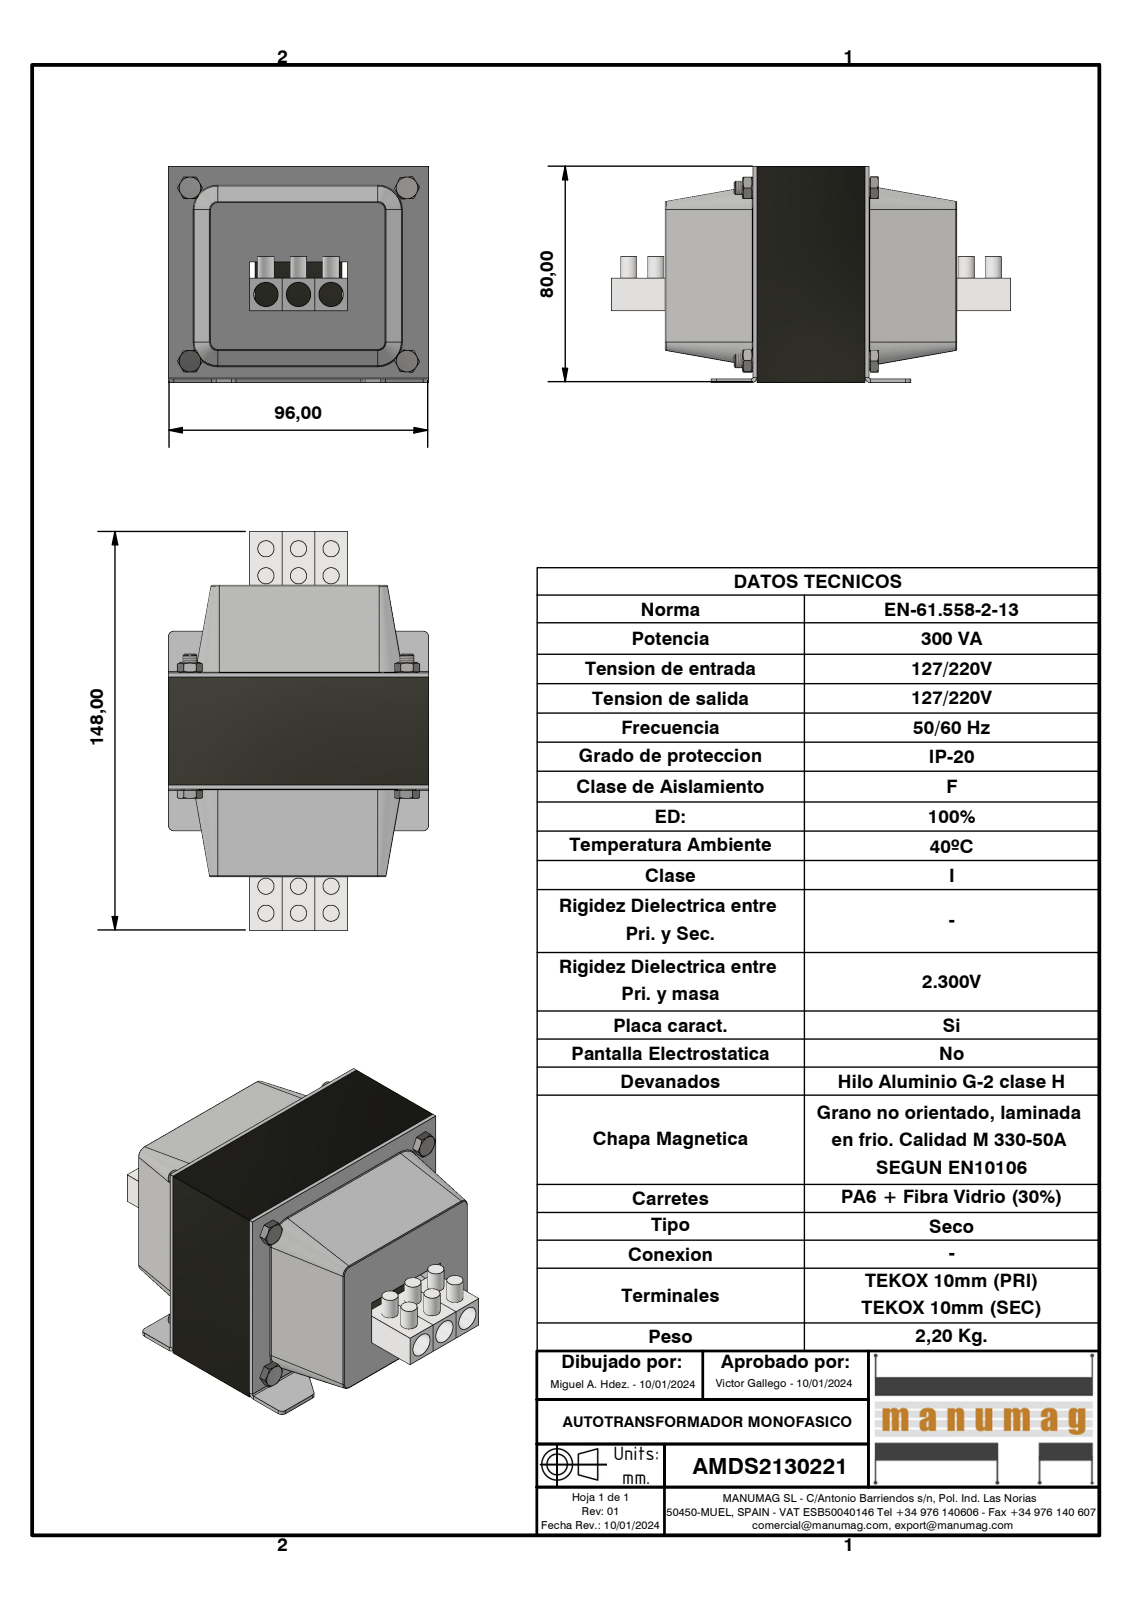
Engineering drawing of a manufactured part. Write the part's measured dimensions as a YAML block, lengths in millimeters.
part_name: "AMDS2130221; DIN 933 - M5 x 50; DIN 934 - M5 x 0,8; TAPA RC32 VENTANA 3 ELEMENTOS 10 CON FICHAS (+4 more)"
step_written_by: "Autodesk Inventor 2023 (AUTOMOTIVE_DESIGN)"
units: millimeters
bodies: {solids: 17, faces: 352, planar: 194, cylindrical: 78, other: 80}
overall_size: [148, 96, 80]
volume: 284535
surface_area: 117805
round_holes:
  - {diameter: 4.13, count: 4}
  - {diameter: 5, count: 4}
  - {diameter: 5.5, count: 4}
  - {diameter: 9, count: 3}
round_bosses_or_shafts:
  - {diameter: 6, count: 12}
  - {diameter: 6.7, count: 4}
  - {diameter: 4.57, count: 4}
partial_cylinders:
  - {radius: 0.38, count: 16}
  - {radius: 2, count: 14}
  - {radius: 0.5, count: 2}
face_to_face_distances: [1.5, 32.5, 74, 16, 40, 64, 80, 34, 72.5, 32]
hole_center_spacings: [12, 37.29, 46.97, 48.31, 56.12, 57.54, 64, 65.22]
